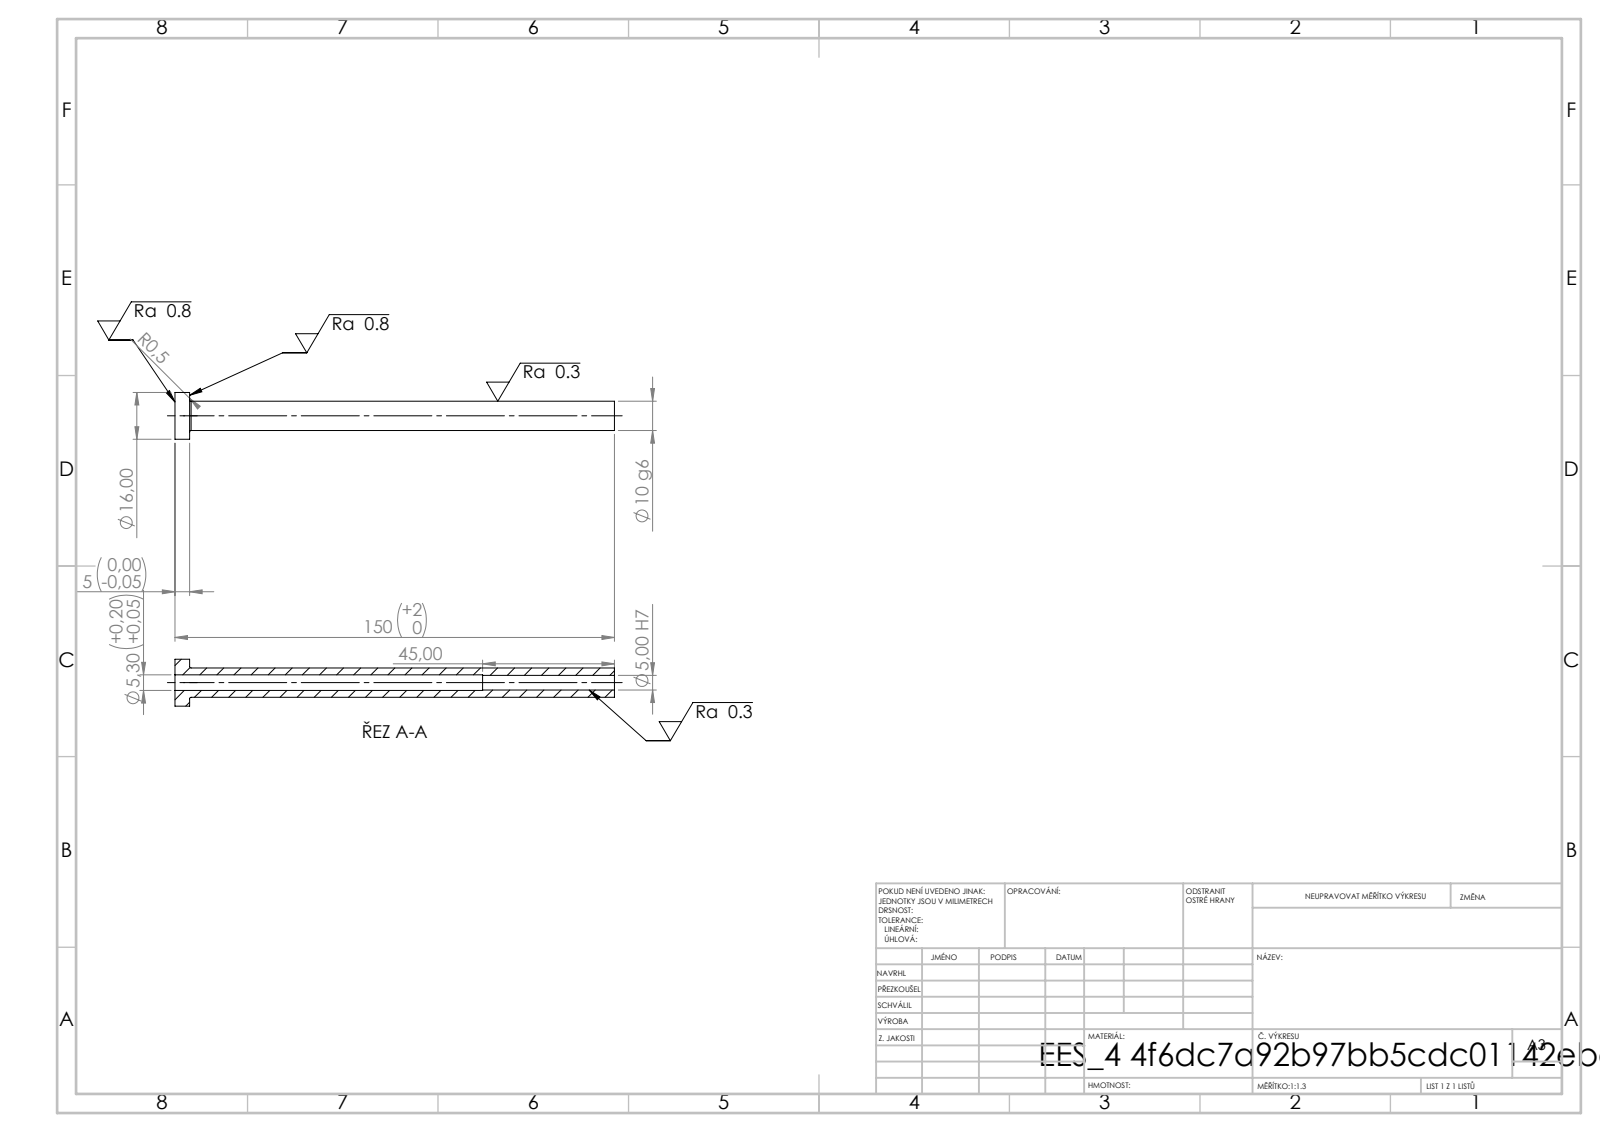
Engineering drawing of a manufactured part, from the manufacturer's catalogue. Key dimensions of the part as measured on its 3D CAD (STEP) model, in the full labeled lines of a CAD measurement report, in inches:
STEP written by: SolidWorks 2019 (CONFIG_CONTROL_DESIGN)
Units: inches
Bodies: 1 solid, 14 faces (4 planar, 8 cylindrical, 2 other)
Overall size (bounding box): 5.906 × 0.63 × 0.63
Volume: 0.561 in³ · Surface area: 11.81 in²
Round holes (diameter × count): ⌀0.197 ×1, ⌀0.209 ×1
Round bosses / shafts (diameter × count): ⌀0.63 ×1, ⌀0.394 ×1
Main face-to-face distances: 0.197, 5.906, 5.709, 4.134, 3.937, 1.772
